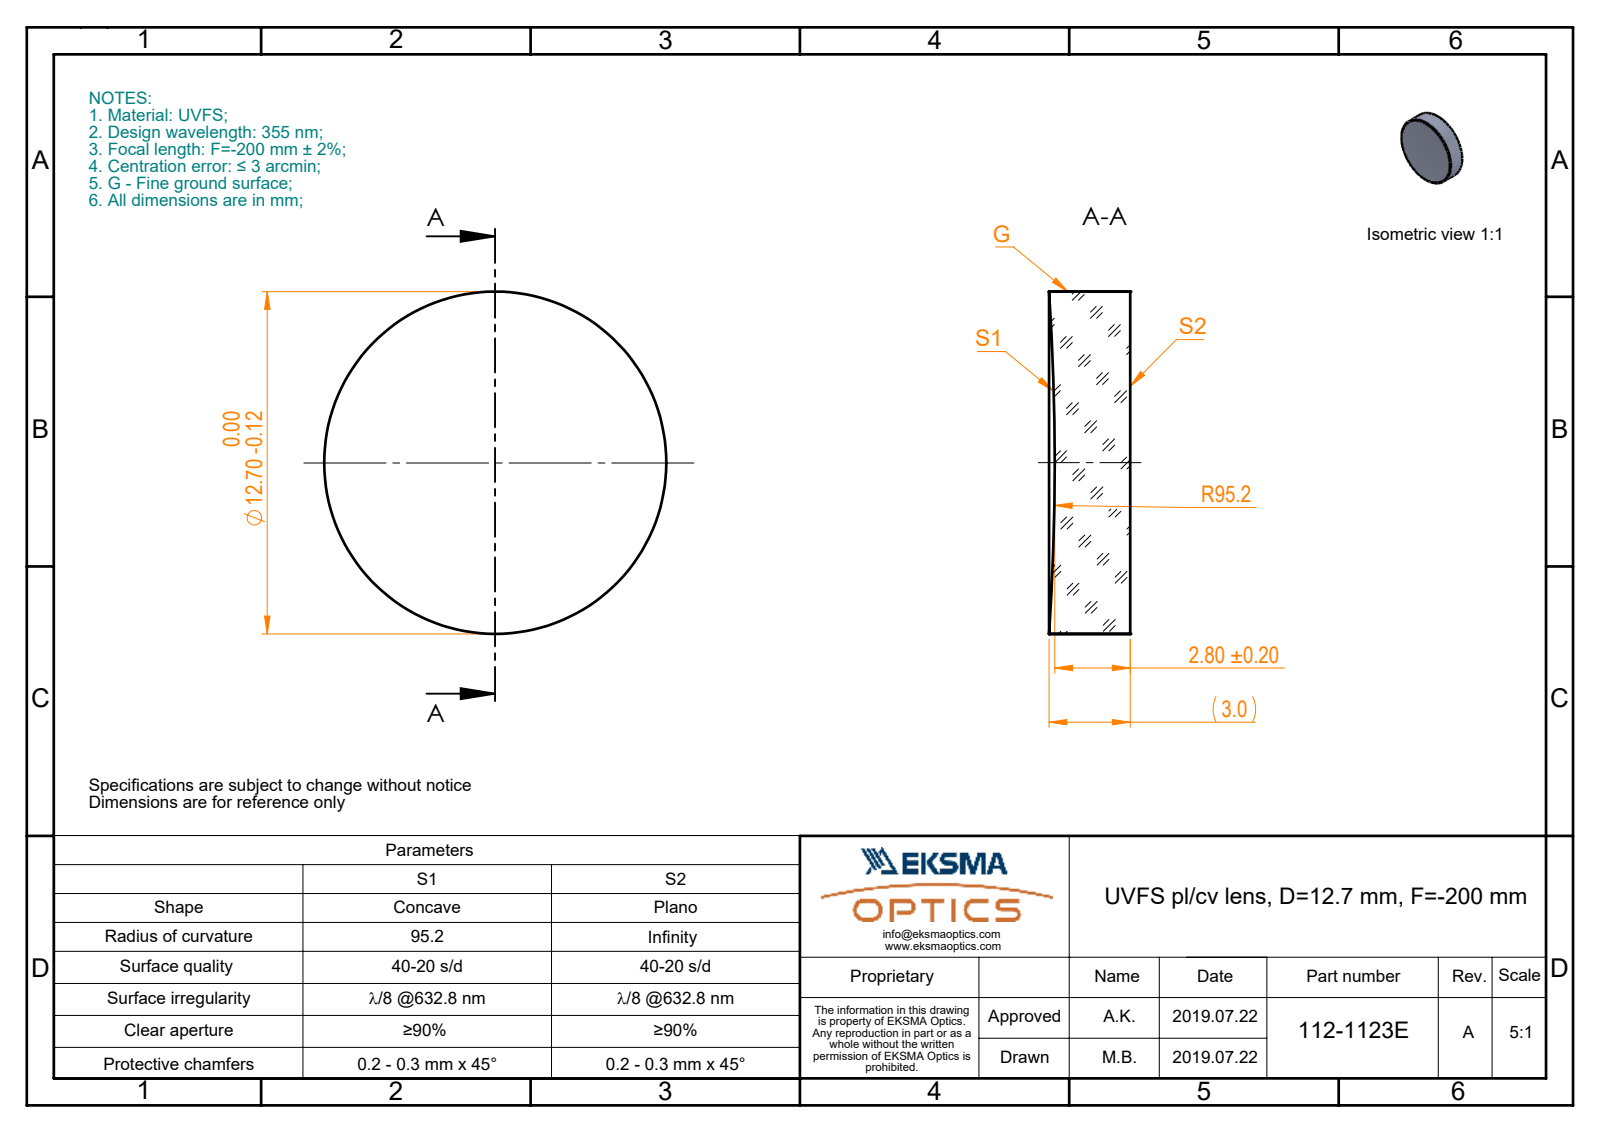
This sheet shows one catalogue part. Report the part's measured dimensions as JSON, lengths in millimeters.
{"part_name": "112-1123E UVFS pl-cv 12.7 F-200", "step_written_by": "SolidWorks 2017 (CONFIG_CONTROL_DESIGN)", "units": "millimeters", "bodies": {"solids": 1, "faces": 5, "planar": 1, "cylindrical": 2, "other": 2}, "overall_size": [12.7, 12.7, 3.01], "volume_mm3": 368, "surface_area_mm2": 374, "round_bosses_or_shafts": [[12.7, 1]]}
